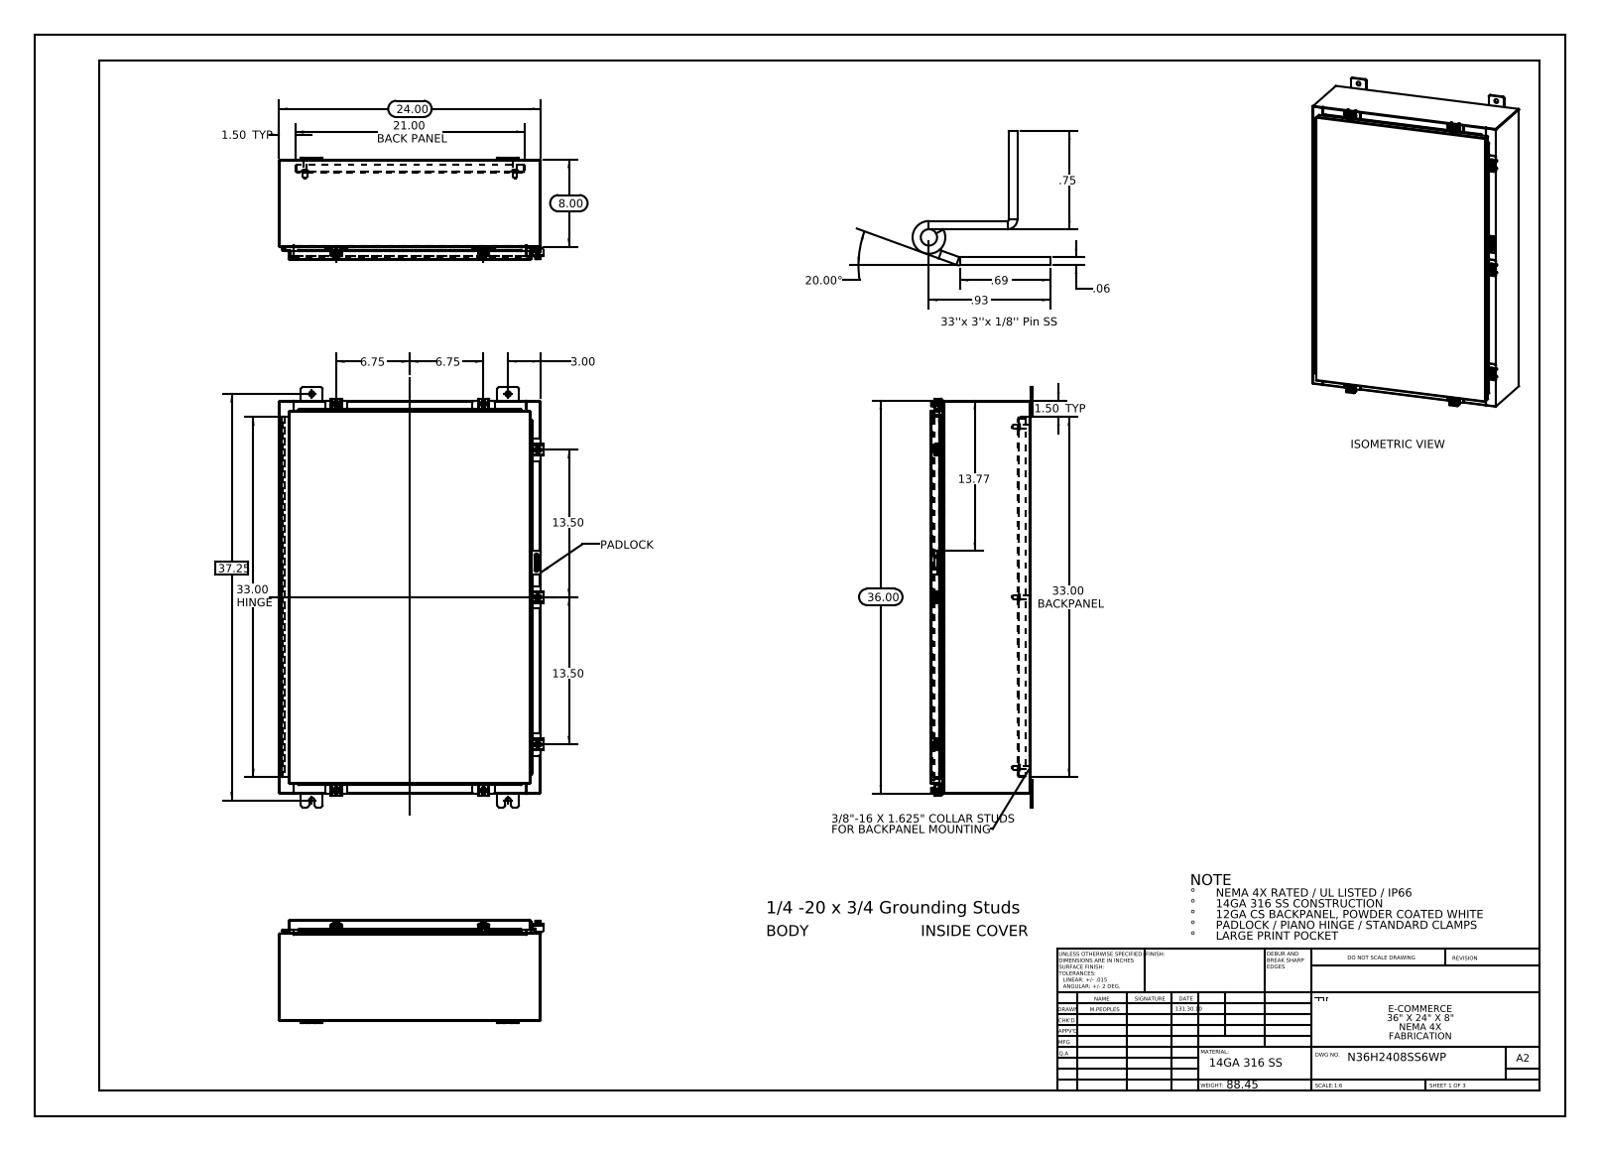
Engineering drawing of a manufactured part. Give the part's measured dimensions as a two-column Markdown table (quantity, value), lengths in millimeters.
| quantity | value |
| --- | --- |
| part name | N36H2408SS6WP Clamp Top; N36H2408SS6WP Backpanel; N36H2408SS6WP Cover; N36H2408SS6WP 22104005_DEFAULT (+8 more) |
| STEP written by | SolidWorks 2013 (CONFIG_CONTROL_DESIGN) |
| units | millimeters |
| bodies | 54 solids, 2184 faces (1138 planar, 922 cylindrical, 124 other) |
| overall size | 977.9 × 615 × 238.5 |
| volume | 5 090 000 mm³ |
| surface area | 4 998 000 mm² |
| round holes (diameter × count) | 12.7 × 10, 5.4 × 7, 6.6 × 7, 3.2 × 2, 3.2 × 1 |
| round bosses / shafts (diameter × count) | 6.4 × 8, 12.7 × 7, 10.1 × 7, 15.9 × 6, 9.5 × 6, 8.4 × 6 |
| partial cylindrical surfaces (radius × count) | 1.5 × 34, 0.3 × 27, 4.8 × 24, 2.2 × 21, 3 × 14, 3.6 × 14, 1.3 × 11, 2 × 10 |
| main face-to-face distances | 1.9, 231.8, 233.7, 229.9, 2.6, 25.4, 27.3, 204.5, 206.4, 29.9 |
| hole center spacings | 342.9, 396.9, 456.1, 629.7, 850.2, 943.7, 489, 47.2 |
